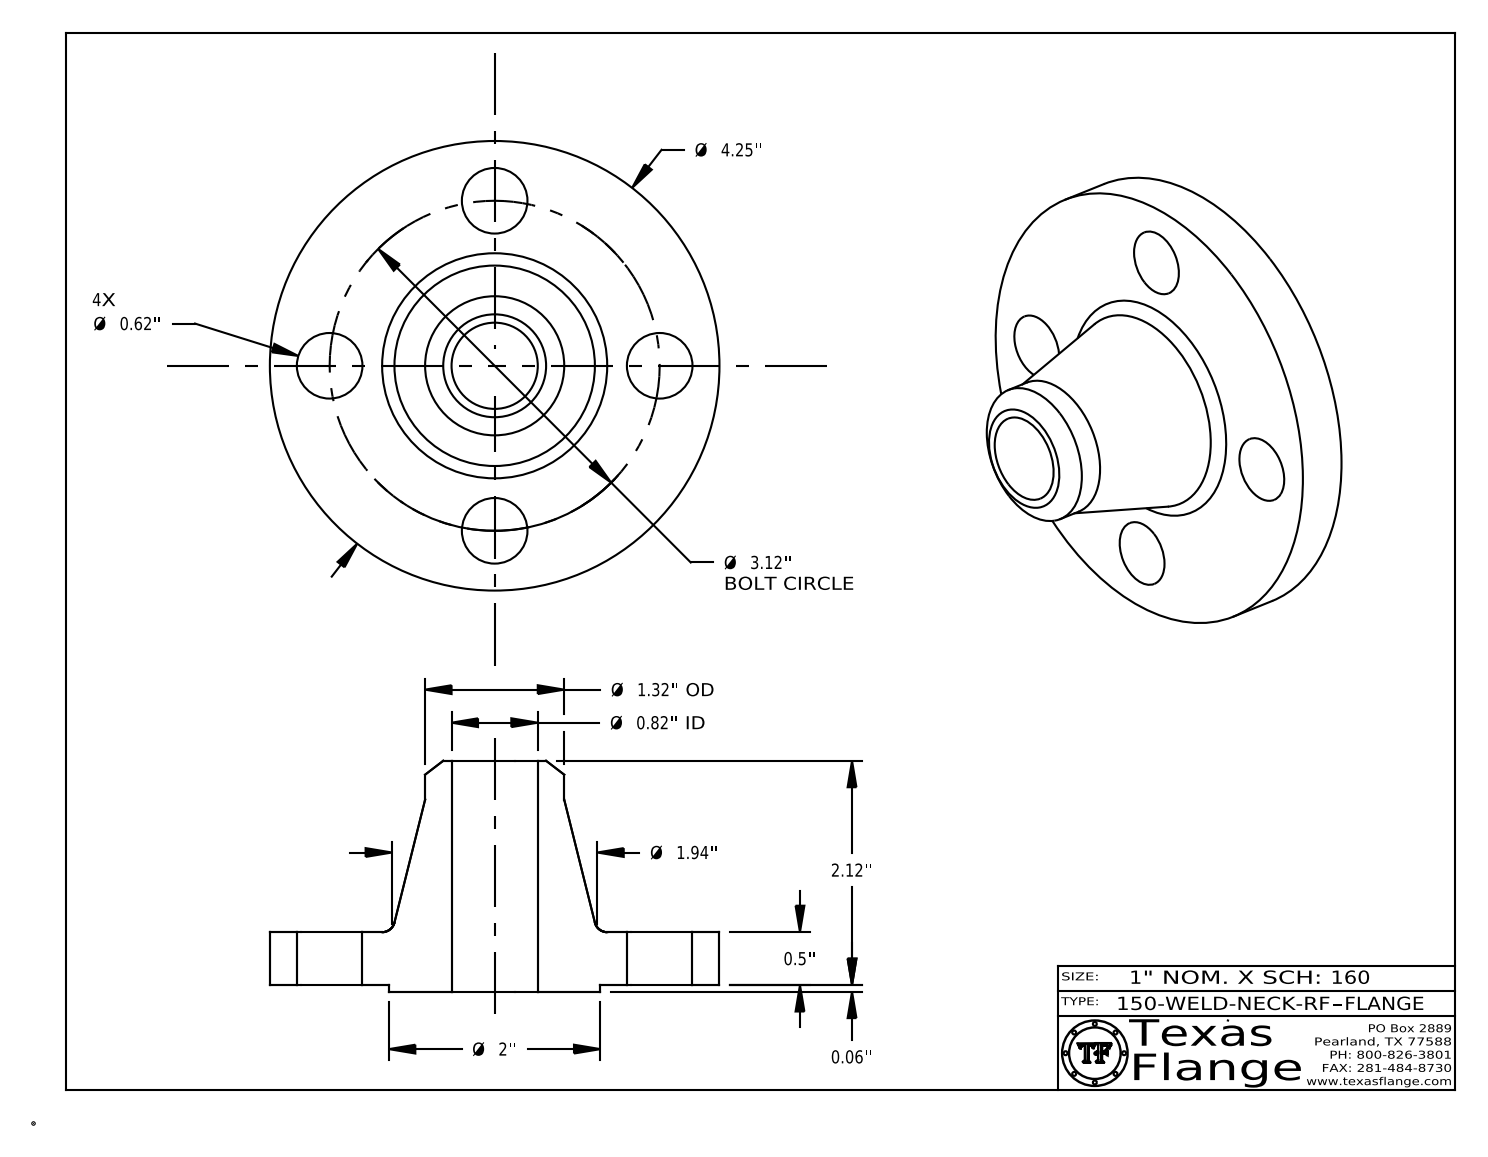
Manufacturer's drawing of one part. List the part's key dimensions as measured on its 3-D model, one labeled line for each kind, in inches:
Part name (STEP PRODUCT): 150-WELD-NECK-RF
STEP written by: CATIA V5 STEP AP214 (AUTOMOTIVE_DESIGN)
Units: inches
Bodies: 1 solid, 411 faces (369 planar, 36 cylindrical, 6 other)
Overall size (bounding box): 4.25 × 4.25 × 2.183
Volume: 8.651 in³ · Surface area: 47.53 in²
Round holes (diameter × count): ⌀0.62 ×4, ⌀0.495 ×1, ⌀0.815 ×1
Round bosses / shafts (diameter × count): ⌀0.03 ×8, ⌀4.25 ×1, ⌀2 ×1, ⌀1.315 ×1, ⌀0.39 ×1
Main face-to-face distances: 0.5, 0.063, 0.563, 2.183, 2.12, 1.62, 0.548, 0.485, 0.015, 1.635
Hole centre spacings: 1.56, 2.206, 1.194, 2.882, 3.12, 1.56
